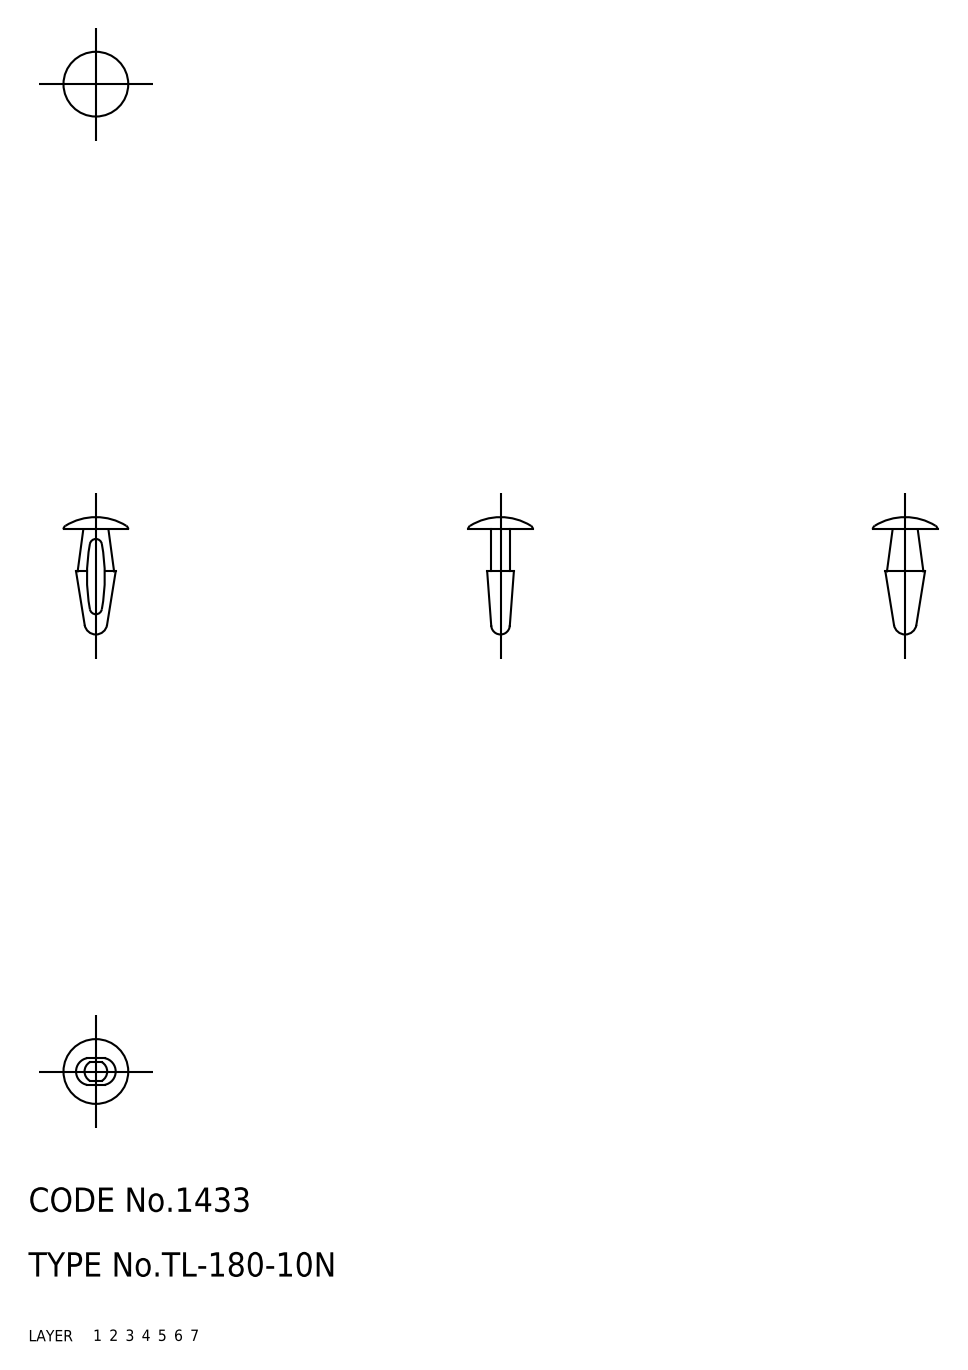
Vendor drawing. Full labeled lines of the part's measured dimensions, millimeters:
Part name (STEP PRODUCT): fastener
STEP written by: CADfix (AUTOMOTIVE_DESIGN)
Units: millimetres
Bodies: 1 solid, 34 faces (0 planar, 0 cylindrical, 34 other)
Overall size (bounding box): 14.5 × 8 × 8
Volume: 127 mm³ · Surface area: 275 mm²
